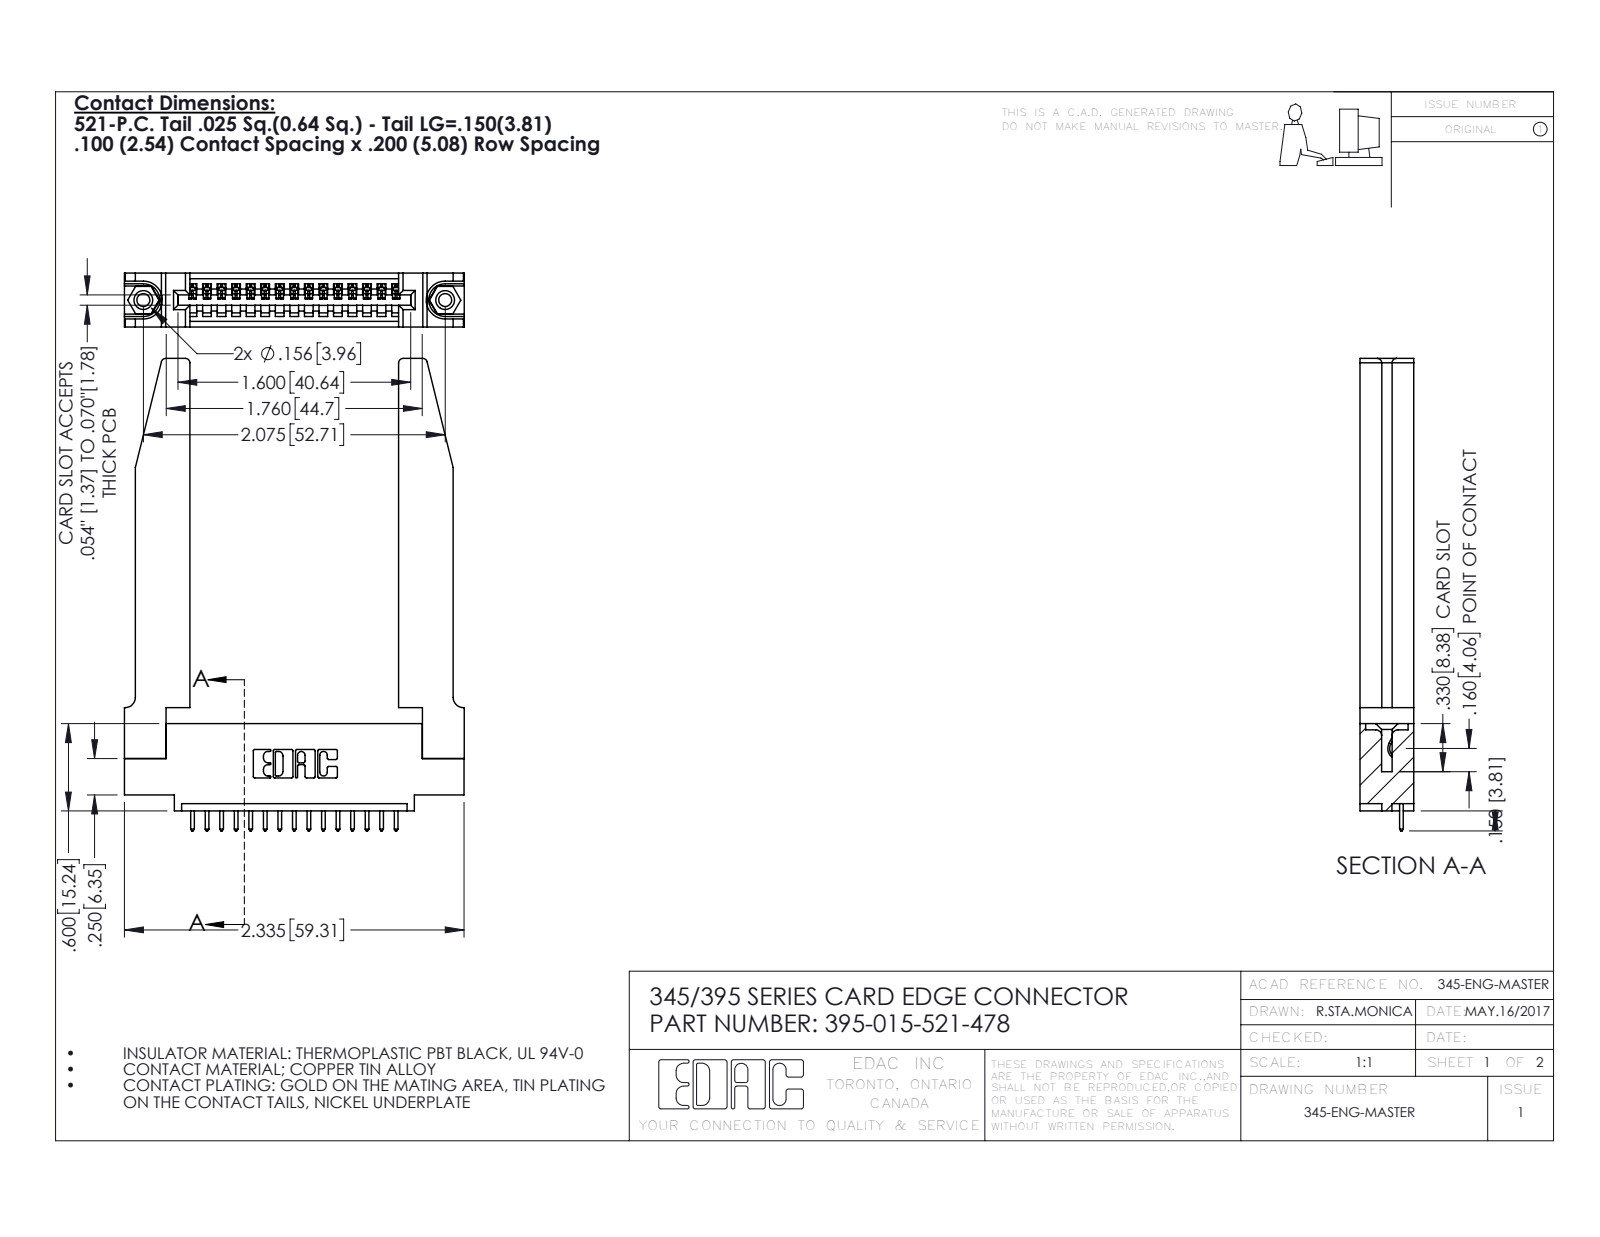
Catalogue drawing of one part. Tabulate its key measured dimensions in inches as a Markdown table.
| quantity | value |
| --- | --- |
| part name | 345-250-001_345-250-001-102; 395-015-521-478; 345 Part_0.110 Offset - 0.156 Dia-TH; 345-292-001_345-293-121 (+1 more) |
| STEP written by | SolidWorks 2016 (CONFIG_CONTROL_DESIGN) |
| units | inches |
| bodies | 20 solids, 1234 faces (826 planar, 356 cylindrical, 52 other) |
| overall size | 3.247 × 2.336 × 0.37 |
| volume | 0.798 in³ |
| surface area | 20.82 in² |
| round holes (diameter × count) | 0.089 × 2, 0.125 × 2, 0.156 × 2, 0.064 × 1 |
| round bosses / shafts (diameter × count) | 0.155 × 2 |
| partial cylindrical surfaces (radius × count) | 0.006 × 30, 0.01 × 30, 0.01 × 22, 0.03 × 8, 0.007 × 6, 0.031 × 6, 0.026 × 3, 0.031 × 2 |
| main face-to-face distances | 0.37, 0.072, 0.298, 0.15, 0.148, 0.22, 0.077, 0.2, 0.098, 0.272 |
| hole center spacings | 0.27, 1.842, 2.075 |
